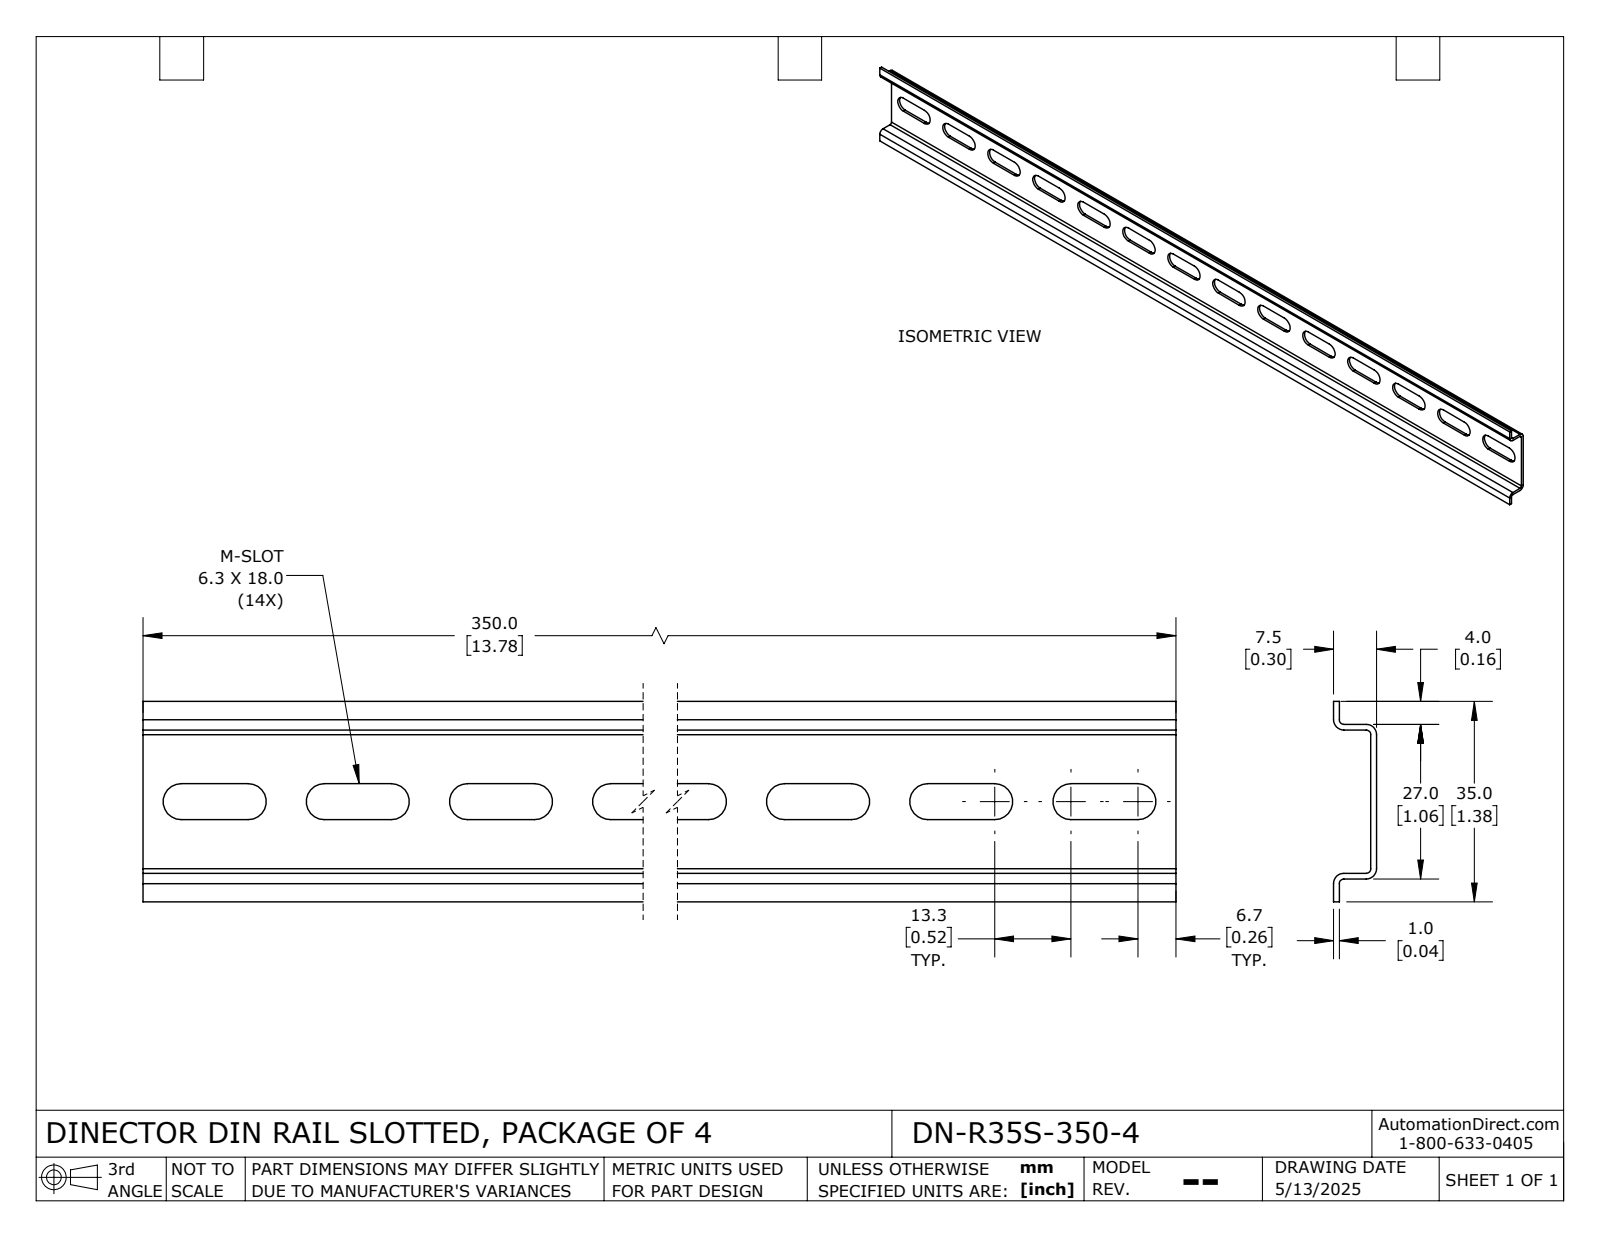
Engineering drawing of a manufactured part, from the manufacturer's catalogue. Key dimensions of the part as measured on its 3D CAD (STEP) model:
Part name (STEP PRODUCT): DN-R35S-350-4_Default
STEP written by: SolidWorks 2024 (CONFIG_CONTROL_DESIGN)
Units: millimetres
Bodies: 1 solid, 78 faces (42 planar, 36 cylindrical, 0 other)
Overall size (bounding box): 350 × 35 × 7.5
Volume: 14 550 mm³ · Surface area: 30 497 mm²
Partial cylindrical surfaces — rounded edges, fillets, slot ends (radius × count): R3.15 ×28, R0.8 ×4, R1.8 ×4
Main face-to-face distances: 1, 6.5, 26, 7.5, 5.5, 27, 25, 4, 5, 30
